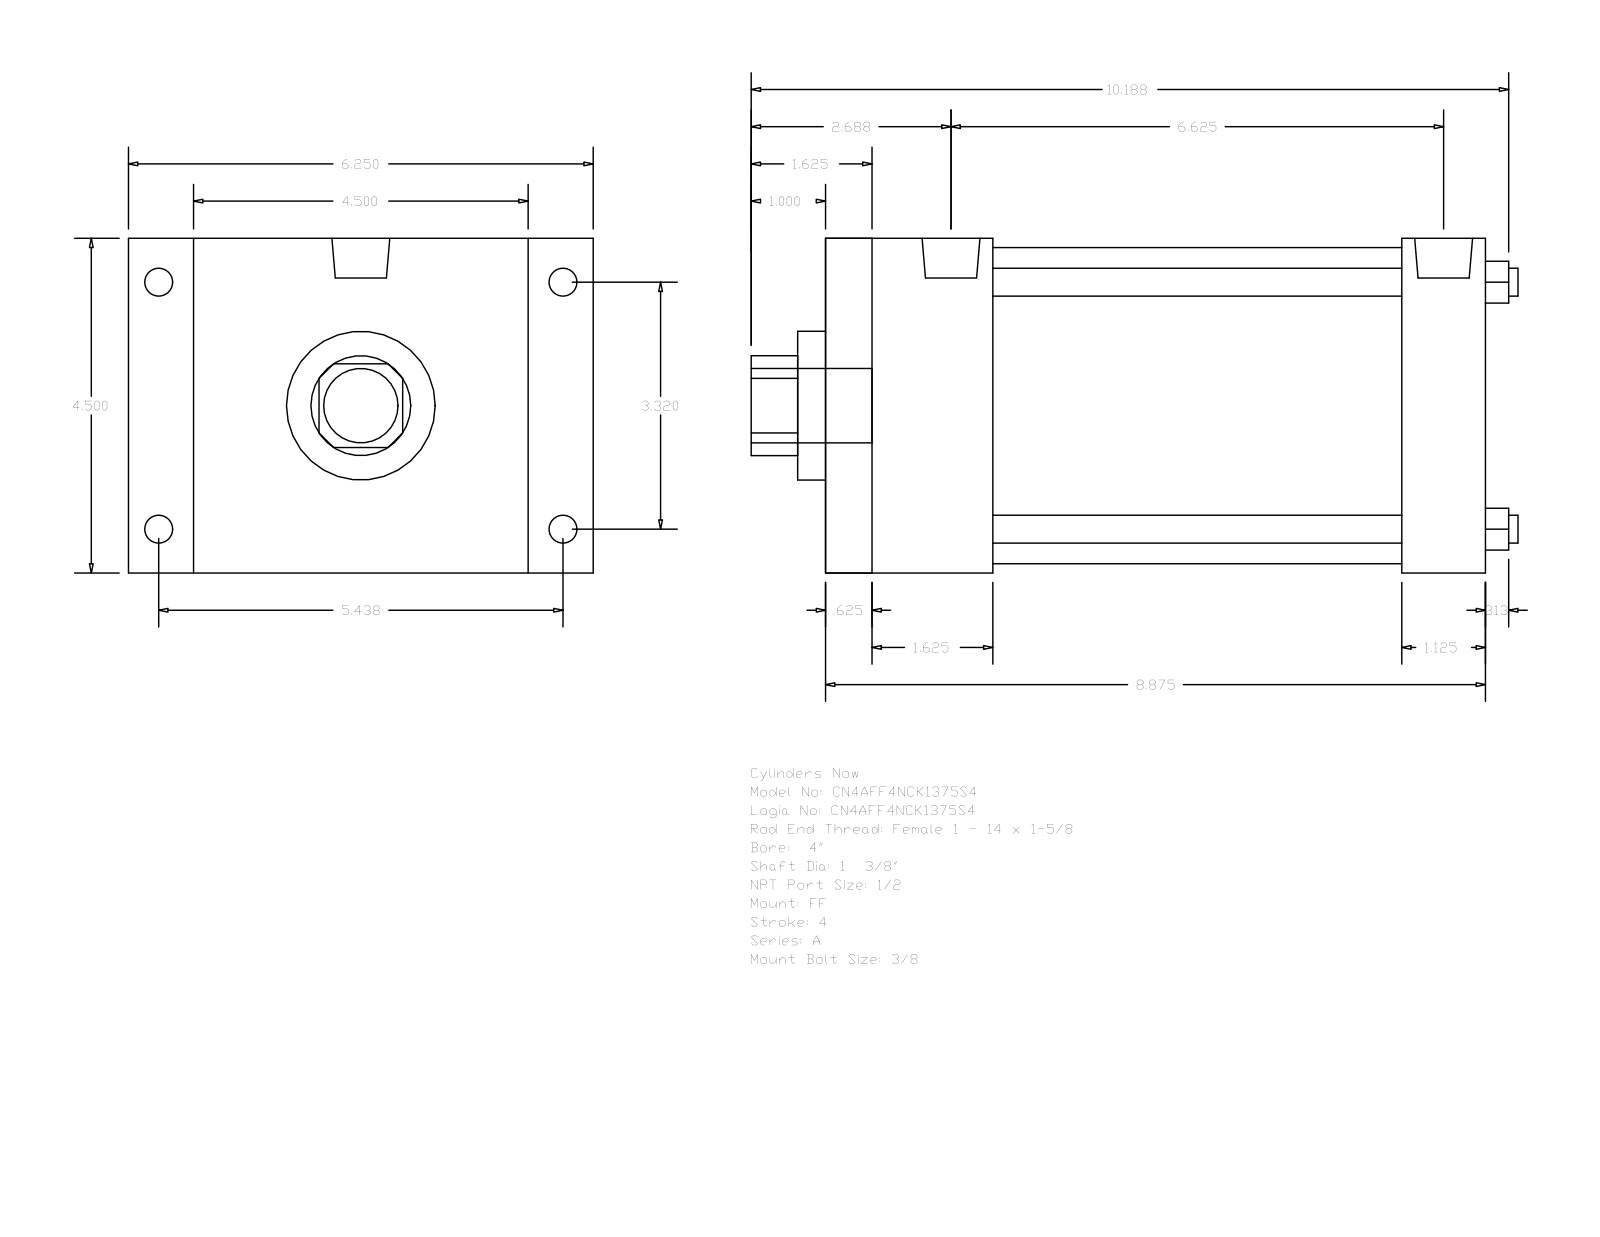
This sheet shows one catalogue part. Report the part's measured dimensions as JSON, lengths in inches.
{"part_name": "A_FF__0400_1.375", "step_written_by": "GSSL Pune (CONFIG_CONTROL_DESIGN)", "units": "inches", "bodies": {"solids": 0, "faces": 92, "planar": 64, "cylindrical": 28, "other": 0}, "overall_size": [10.313, 6.25, 4.5], "round_holes": [[0.375, 4], [1.375, 1], [2, 1], [4.25, 1]], "round_bosses_or_shafts": [[0.375, 4], [0.344, 4], [0.778, 2], [1, 1]], "partial_cylinders_radius": [[0.672, 1]], "face_to_face_distances": [4.5, 8.875, 8.25, 0.625, 1.125, 0.875, 5.375, 7.75, 7.125, 2.25], "hole_center_spacings": [2.347, 3.32, 4.695]}
